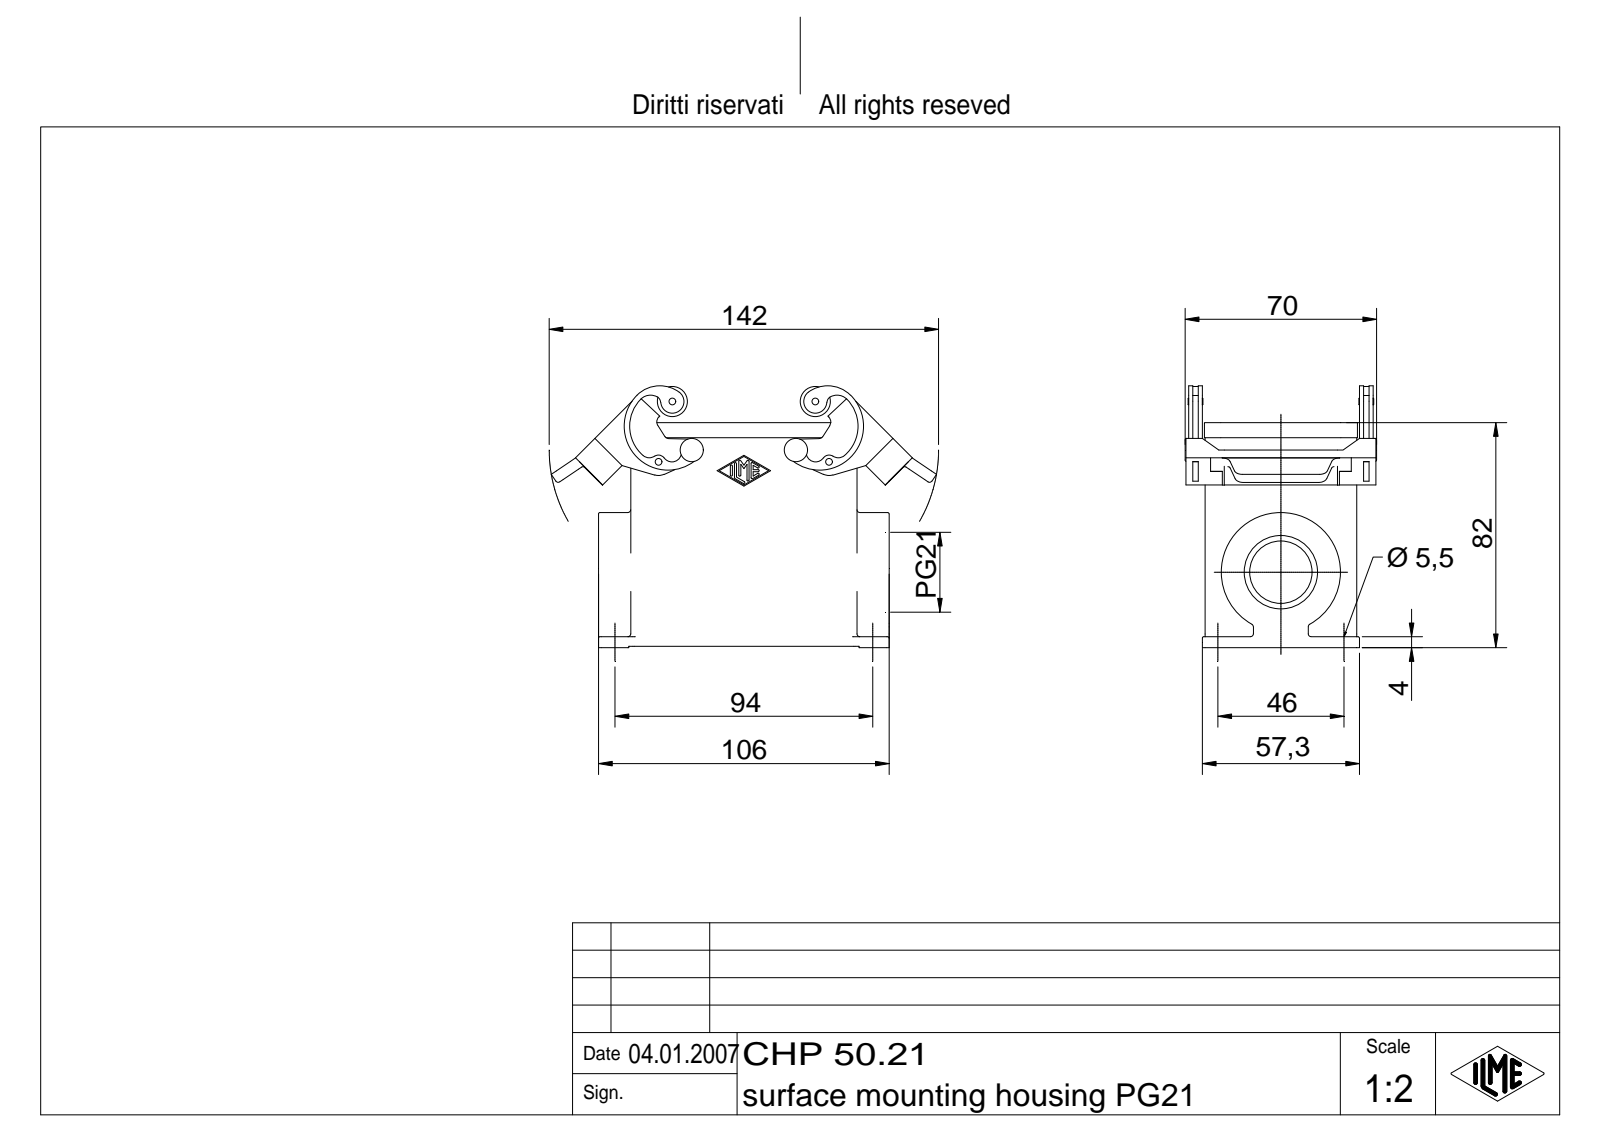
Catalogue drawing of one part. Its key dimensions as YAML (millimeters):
part_name: "CHP 50.21"
step_written_by: "Autodesk Inventor 7 (AUTOMOTIVE_DESIGN)"
units: millimeters
bodies: {solids: 1, faces: 911, planar: 196, cylindrical: 295, other: 420}
overall_size: [140.49, 95.44, 69.8]
volume: 162593
surface_area: 76357
round_holes:
  - {diameter: 2, count: 4}
  - {diameter: 2.46, count: 4}
  - {diameter: 3.1, count: 4}
  - {diameter: 2.5, count: 2}
  - {diameter: 5.5, count: 2}
  - {diameter: 22.78, count: 1}
  - {diameter: 26.78, count: 1}
round_bosses_or_shafts:
  - {diameter: 11, count: 2}
  - {diameter: 5, count: 2}
  - {diameter: 3, count: 2}
  - {diameter: 43.5, count: 1}
partial_cylinders:
  - {radius: 1, count: 30}
  - {radius: 0.38, count: 14}
  - {radius: 0.5, count: 14}
  - {radius: 3, count: 12}
  - {radius: 6, count: 8}
  - {radius: 1.5, count: 6}
  - {radius: 2.5, count: 6}
  - {radius: 2, count: 4}
face_to_face_distances: [3, 52.3, 55.3, 49.3, 3.5, 4, 11, 0.75, 79.5, 82.5]
hole_center_spacings: [16, 22.56, 61.24, 66, 67.91, 14.32, 23.6, 30.41]
